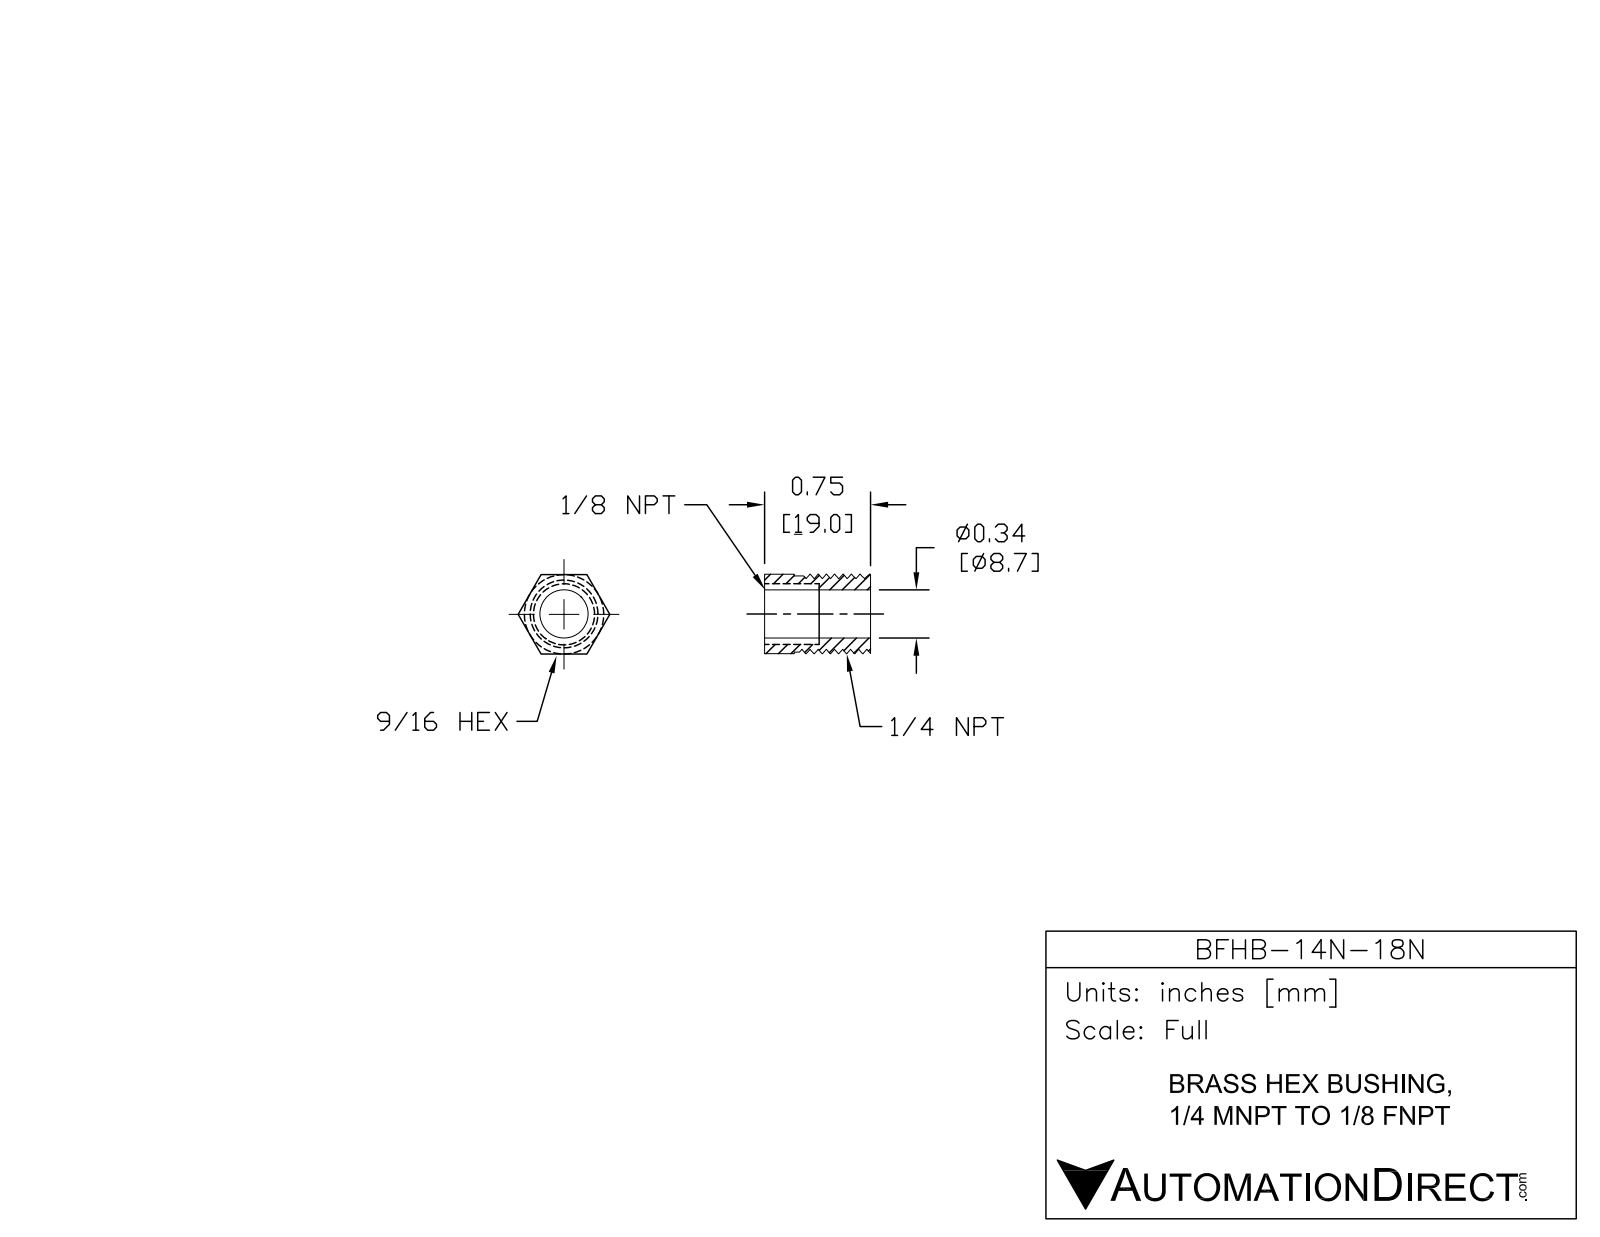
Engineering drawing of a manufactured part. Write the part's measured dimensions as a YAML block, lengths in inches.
part_name: "BFHB-14N-18N"
step_written_by: "SolidWorks 2015 (CONFIG_CONTROL_DESIGN)"
units: inches
bodies: {solids: 1, faces: 58, planar: 10, cylindrical: 31, other: 17}
overall_size: [0.74, 0.65, 0.563]
volume: 0.111
surface_area: 2.969
round_holes:
  - {diameter: 0.325, count: 1}
round_bosses_or_shafts:
  - {diameter: 0.54, count: 1}
face_to_face_distances: [0.562, 0.74, 0.2, 0.54]
